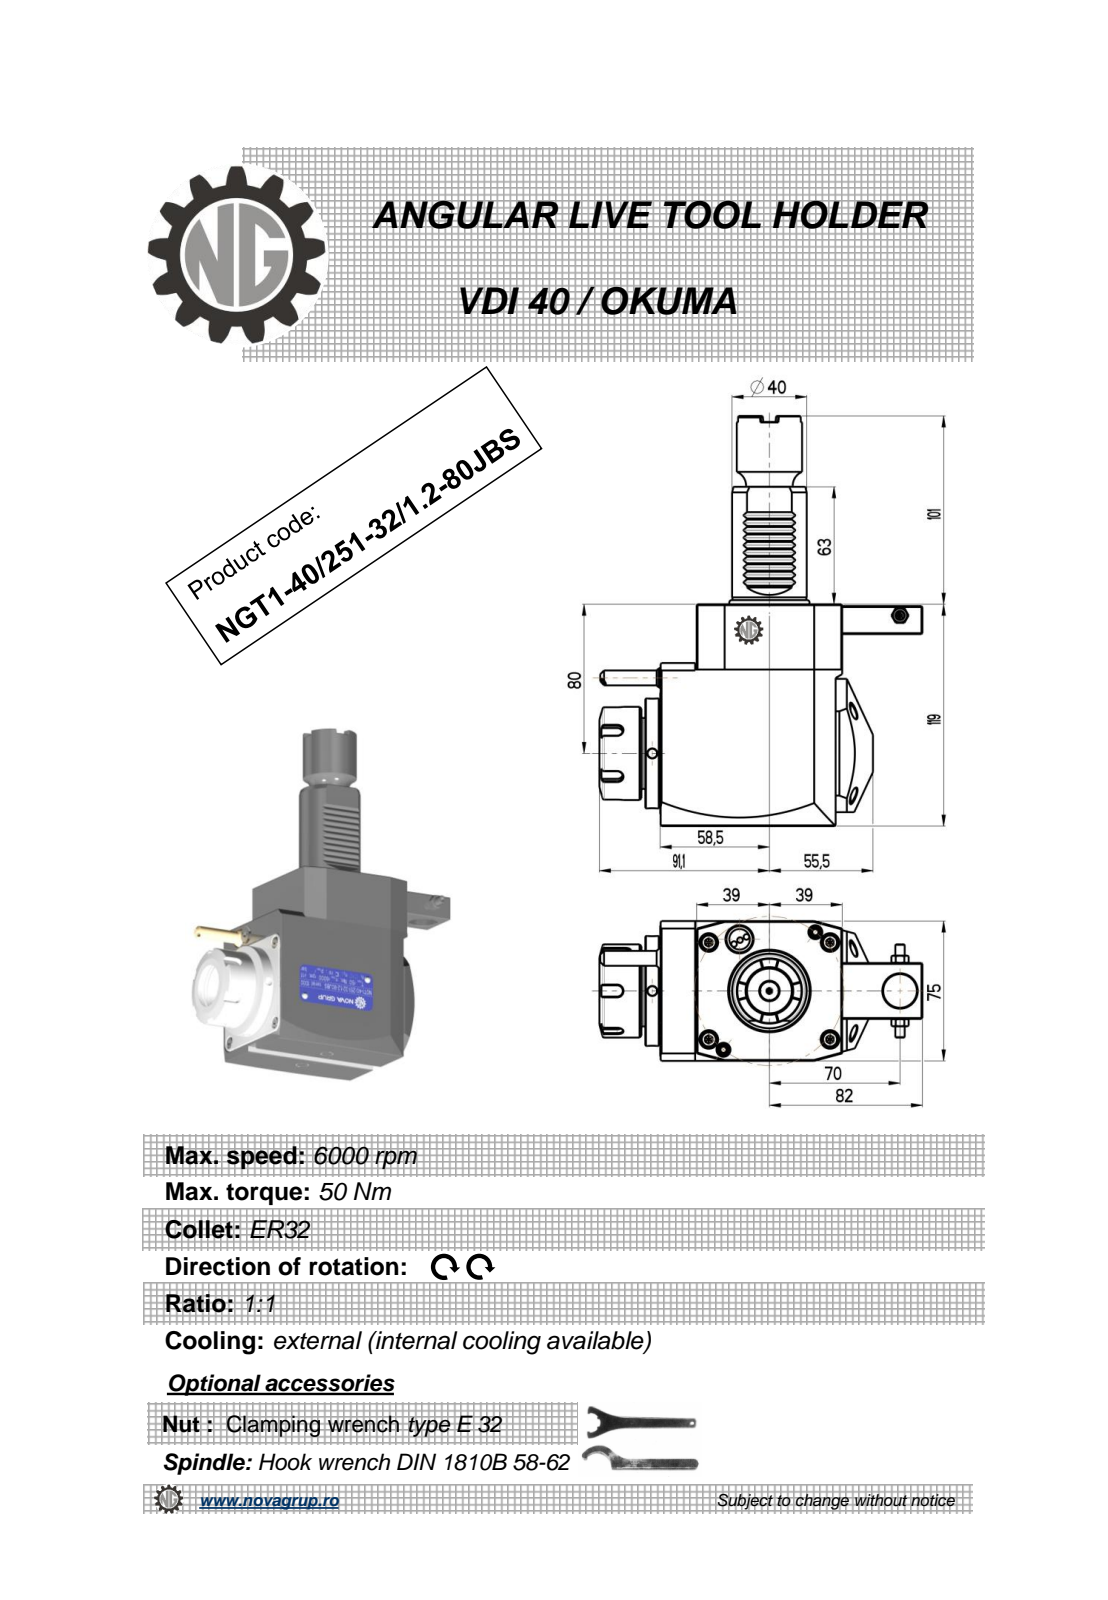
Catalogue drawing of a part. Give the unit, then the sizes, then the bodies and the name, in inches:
Units: inches
Overall size (bounding box): 8.661 × 6.815 × 2.953
Round holes (diameter × count): ⌀0.197 ×3, ⌀0.118 ×1, ⌀0.165 ×1, ⌀0.374 ×1, ⌀0.709 ×1, ⌀0.984 ×1, ⌀1.063 ×1
Round bosses / shafts (diameter × count): ⌀2.323 ×1, ⌀1.969 ×1, ⌀1.85 ×1, ⌀1.614 ×1, ⌀1.575 ×1, ⌀1.378 ×1, ⌀0.394 ×1, ⌀0.353 ×1
Partial cylindrical surfaces — rounded edges, fillets, slot ends (radius × count): R0.01 ×12, R0.012 ×10, R0.008 ×6, R0.118 ×5, R0.236 ×3, R0.228 ×2, R23.622 ×2, R0.02 ×1
Main face-to-face distances: 2.953, 4.685, 0.768, 3.839, 3.071, 0.787, 3.72, 0.039, 0.76, 3.831
Hole centre spacings: 1.436, 1.737, 2.47, 2.756, 2.854, 5.226, 5.983
Volume: 62.79 in³ · Surface area: 130.8 in²
Bodies: 1 solid, 495 faces (224 planar, 98 cylindrical, 173 other)
Part name (STEP PRODUCT): NGT1_40_251_32_1_2_80JBS
STEP written by: PRO/ENGINEER BY PARAMETRIC TECHNOLOGY CORPORATION, 2010280 (CONFIG_CONTROL_DESIGN)
